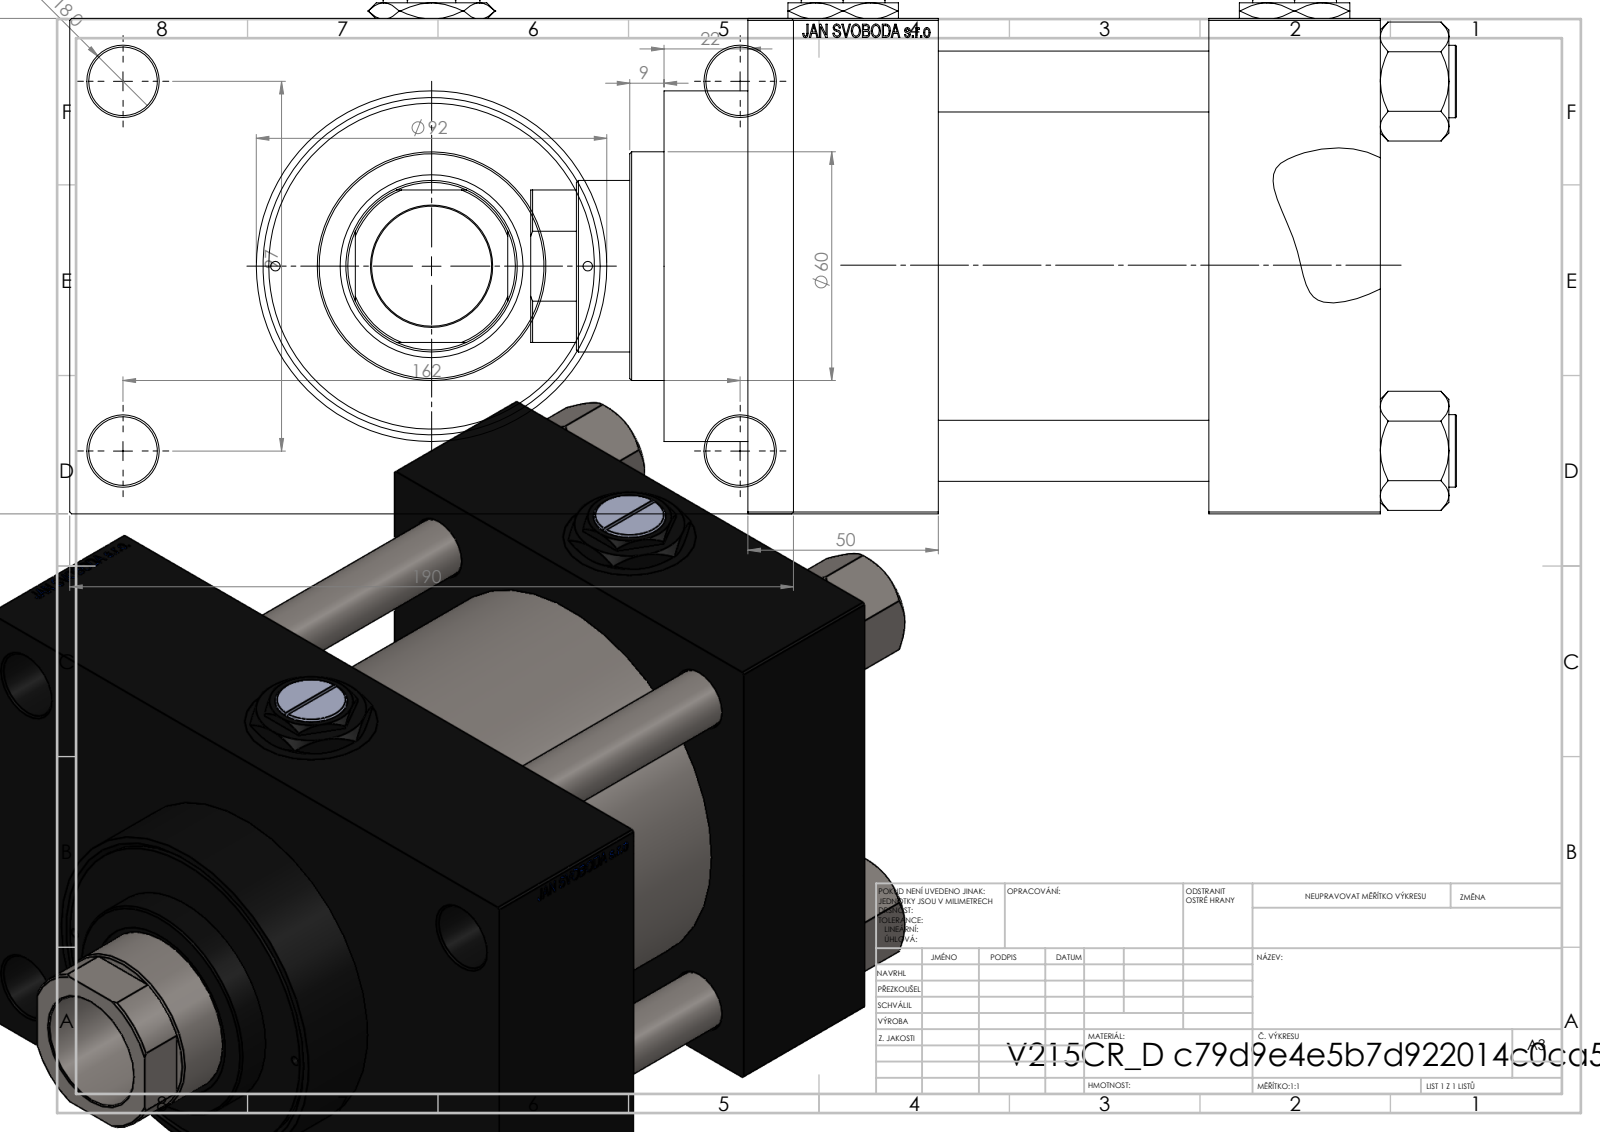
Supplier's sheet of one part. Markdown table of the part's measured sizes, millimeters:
| quantity | value |
| --- | --- |
| part name | V215_VC_A; V215CR_D_Body; V215CR_D_TYCINKA; V215CR_VCP_D (+2 more) |
| STEP written by | SolidWorks 2019 (CONFIG_CONTROL_DESIGN) |
| units | millimeters |
| bodies | 13 solids, 1260 faces (595 planar, 103 cylindrical, 562 other) |
| overall size | 243 × 190 × 137 |
| volume | 2 576 000 mm³ |
| surface area | 361 641 mm² |
| round holes (diameter × count) | 16 × 4, 18 × 4, 26.44 × 4, 35 × 4, 7 × 3, 2.5 × 2, 31.5 × 1, 45 × 1, 48 × 1, 76 × 1, 85.5 × 1, 100 × 1 |
| round bosses / shafts (diameter × count) | 19 × 4, 106 × 1, 92 × 1, 60 × 1 |
| partial cylindrical surfaces (radius × count) | 22 × 1 |
| main face-to-face distances | 45, 130, 116, 71, 166, 121, 50, 30, 160, 20 |
| hole center spacings | 32.55, 49.02, 62.87, 68.52, 94.41, 96.9, 101.73, 102.27 |
